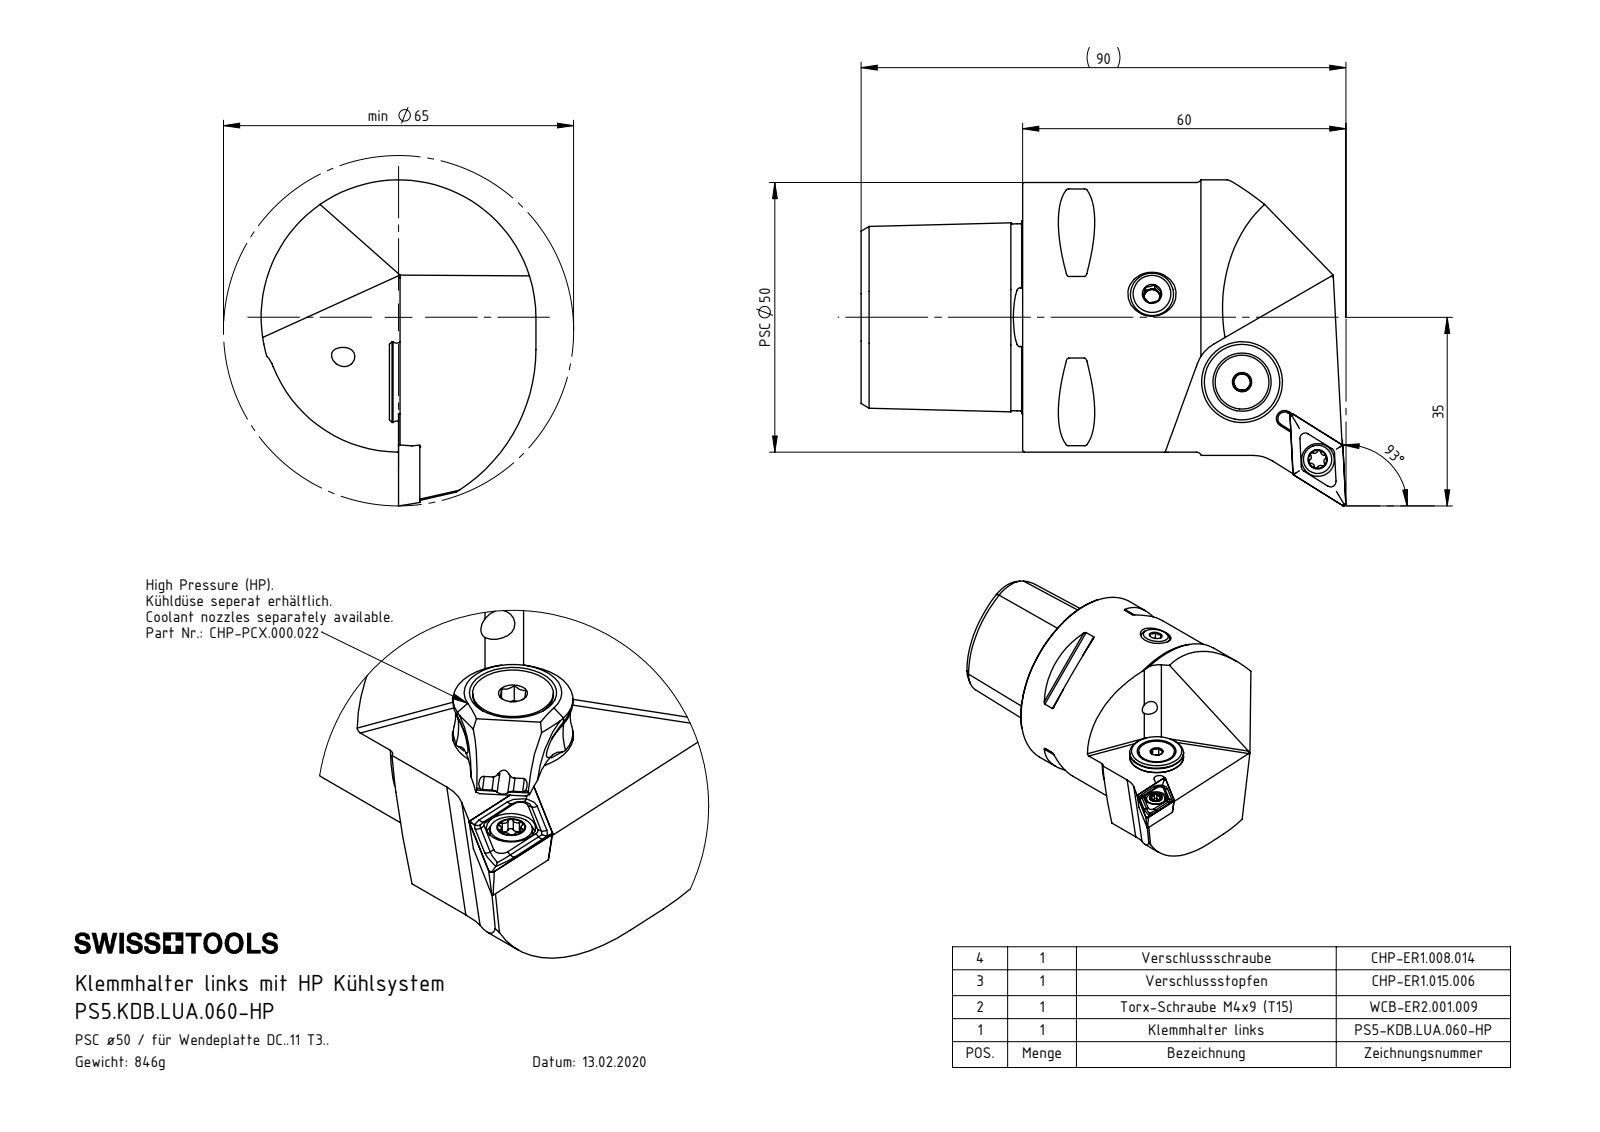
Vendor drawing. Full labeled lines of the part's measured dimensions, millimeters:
Part name (STEP PRODUCT): PS5.KDB.LUA.060-HP; CHP-ER1.015.006_A; ISO 8752 2x8; DIN 3771 - 13x1 (+6 more)
STEP written by: SolidWorks 2017 (AUTOMOTIVE_DESIGN)
Units: millimetres
Bodies: 8 solids, 377 faces (91 planar, 99 cylindrical, 187 other)
Overall size (bounding box): 90 × 60.51 × 51
Volume: 107 839 mm³ · Surface area: 22 697 mm²
Round holes (diameter × count): ⌀4.2 ×3, ⌀6.1 ×2, ⌀1.2 ×1, ⌀2 ×1, ⌀2.5 ×1, ⌀3 ×1, ⌀3.3 ×1, ⌀4 ×1, ⌀4.4 ×1, ⌀5 ×1, ⌀5.2 ×1, ⌀7 ×1
Round bosses / shafts (diameter × count): ⌀50 ×1, ⌀15 ×1, ⌀13.4 ×1, ⌀10 ×1, ⌀8 ×1, ⌀5.5 ×1, ⌀5.25 ×1, ⌀5 ×1
Partial cylindrical surfaces — rounded edges, fillets, slot ends (radius × count): R0.5 ×10, R0.34 ×6, R0.59 ×6, R7 ×2, R1.25 ×1, R4 ×1, R25.5 ×1, R31 ×1
Main face-to-face distances: 30, 4.5, 19.18, 0.83, 3.67, 44.4, 20.7, 21.53, 25.2, 20
Hole centre spacings: 4.5, 16.51, 16.64, 20.05, 20.17, 26, 31.13, 35.56
